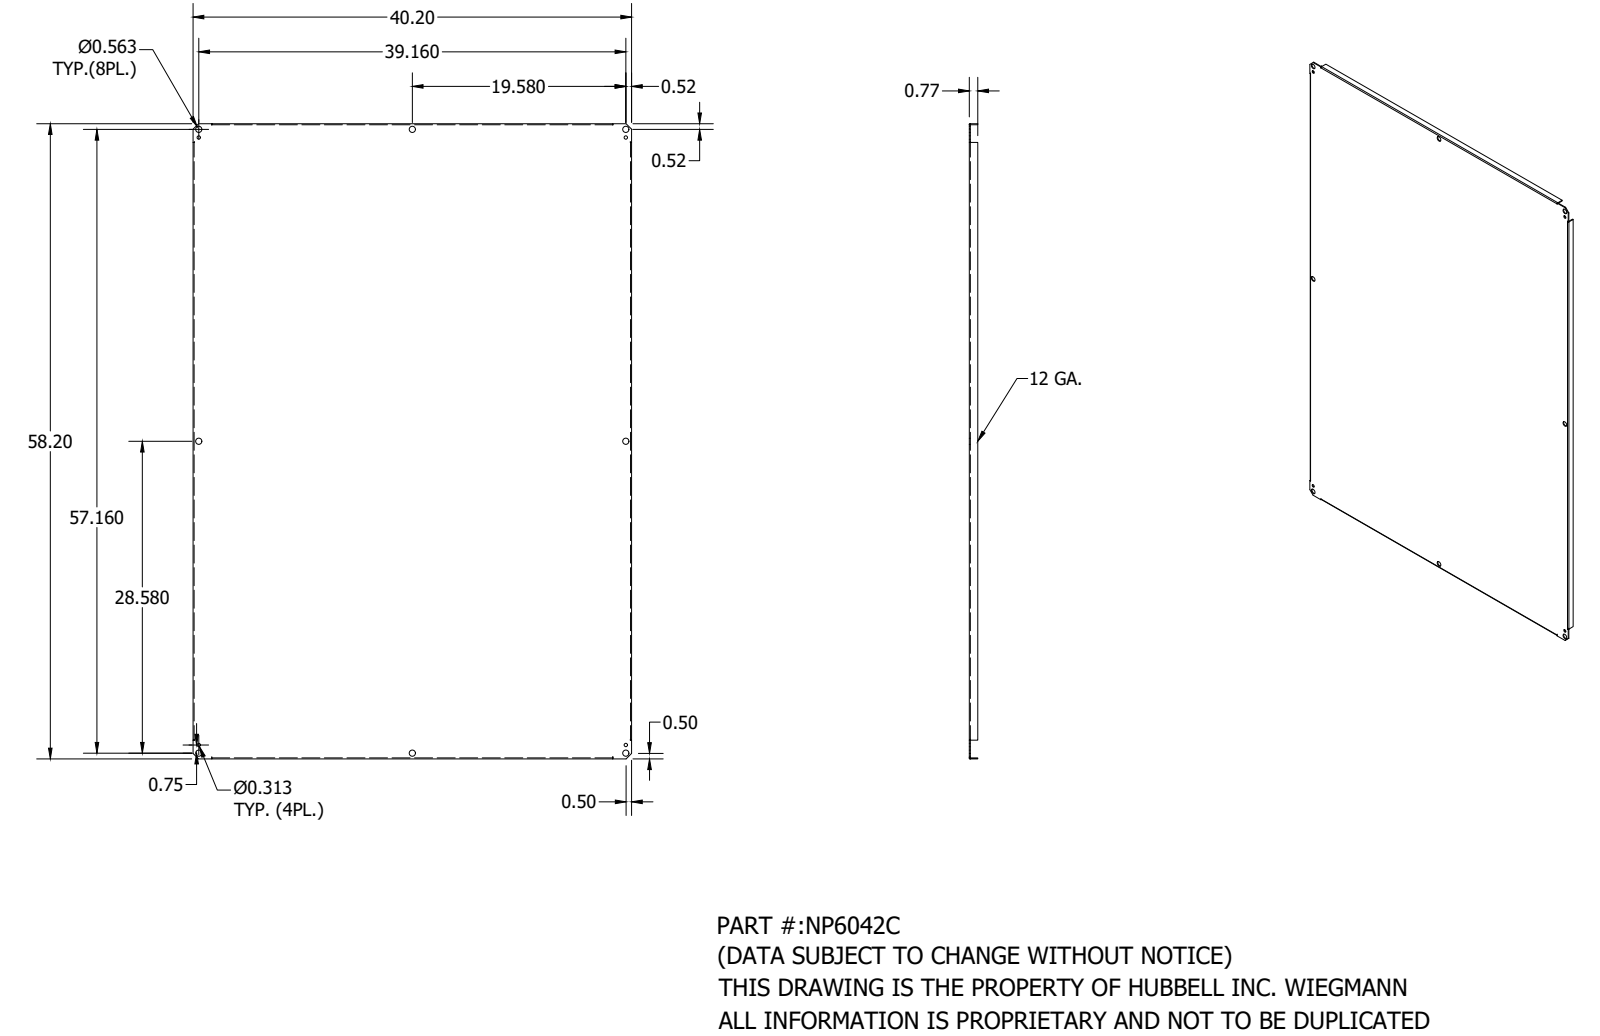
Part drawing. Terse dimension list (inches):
name: NP6042C
written by: Autodesk Inventor 2018 (AUTOMOTIVE_DESIGN)
unit: in
bodies: 1 solid, 70 faces (50 planar, 20 cylindrical, 0 other)
size: 58.2 × 40.2 × 0.774
volume: 230.3 in³; area: 4 934 in²
holes: 8× ⌀0.563, 4× ⌀0.313
rounds: 4× R0.016, 4× R0.109
face distances: 0.094, 40.106, 58.106, 40.2, 40.013, 58.2, 58.013, 0.68, 0.774, 1.718
hole spacings: 39.16, 0.75, 19.58, 19.594, 27.83, 28.58, 34.644, 39.167
